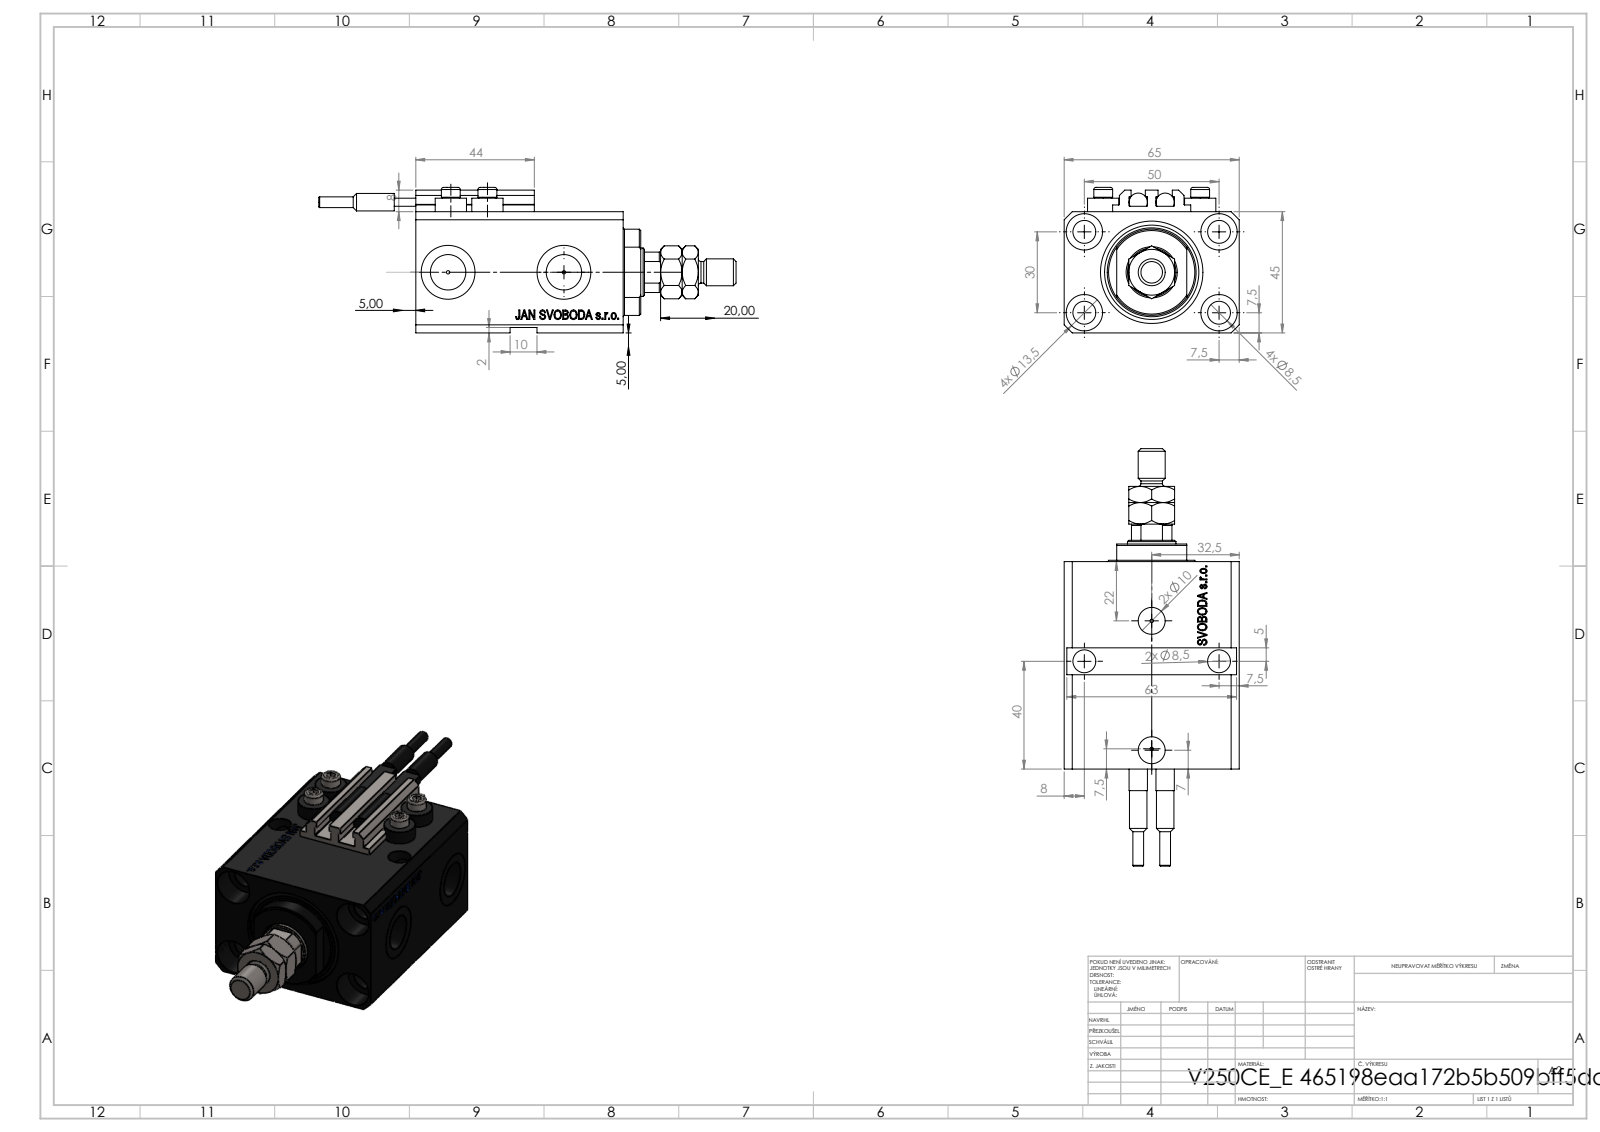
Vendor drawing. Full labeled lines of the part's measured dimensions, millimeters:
Part name (STEP PRODUCT): SWITCH_V250CE; V250CE_E_Body; ALLEN BOLT V250CE; V250CE_VC_E (+2 more)
STEP written by: SolidWorks 2019 (CONFIG_CONTROL_DESIGN)
Units: millimetres
Bodies: 11 solids, 1184 faces (562 planar, 154 cylindrical, 468 other)
Overall size (bounding box): 155 × 65 × 54
Volume: 204 218 mm³ · Surface area: 64 810 mm²
Round holes (diameter × count): ⌀8.5 ×7, ⌀1.25 ×4, ⌀4 ×4, ⌀13.5 ×4, ⌀10 ×2, ⌀13.16 ×2, ⌀20 ×2, ⌀18 ×1, ⌀25 ×1, ⌀38 ×1
Round bosses / shafts (diameter × count): ⌀11.6 ×4, ⌀7 ×4, ⌀6.8 ×2, ⌀6.5 ×2, ⌀4 ×2, ⌀10 ×1, ⌀8 ×1
Partial cylindrical surfaces — rounded edges, fillets, slot ends (radius × count): R0.2 ×10, R8.5 ×1, R16 ×1
Main face-to-face distances: 45, 65, 14, 63, 2, 3, 77, 6.9, 47, 5
Hole centre spacings: 29.15, 50, 13.6, 15.12, 18.81, 18.97, 26.22, 26.61
